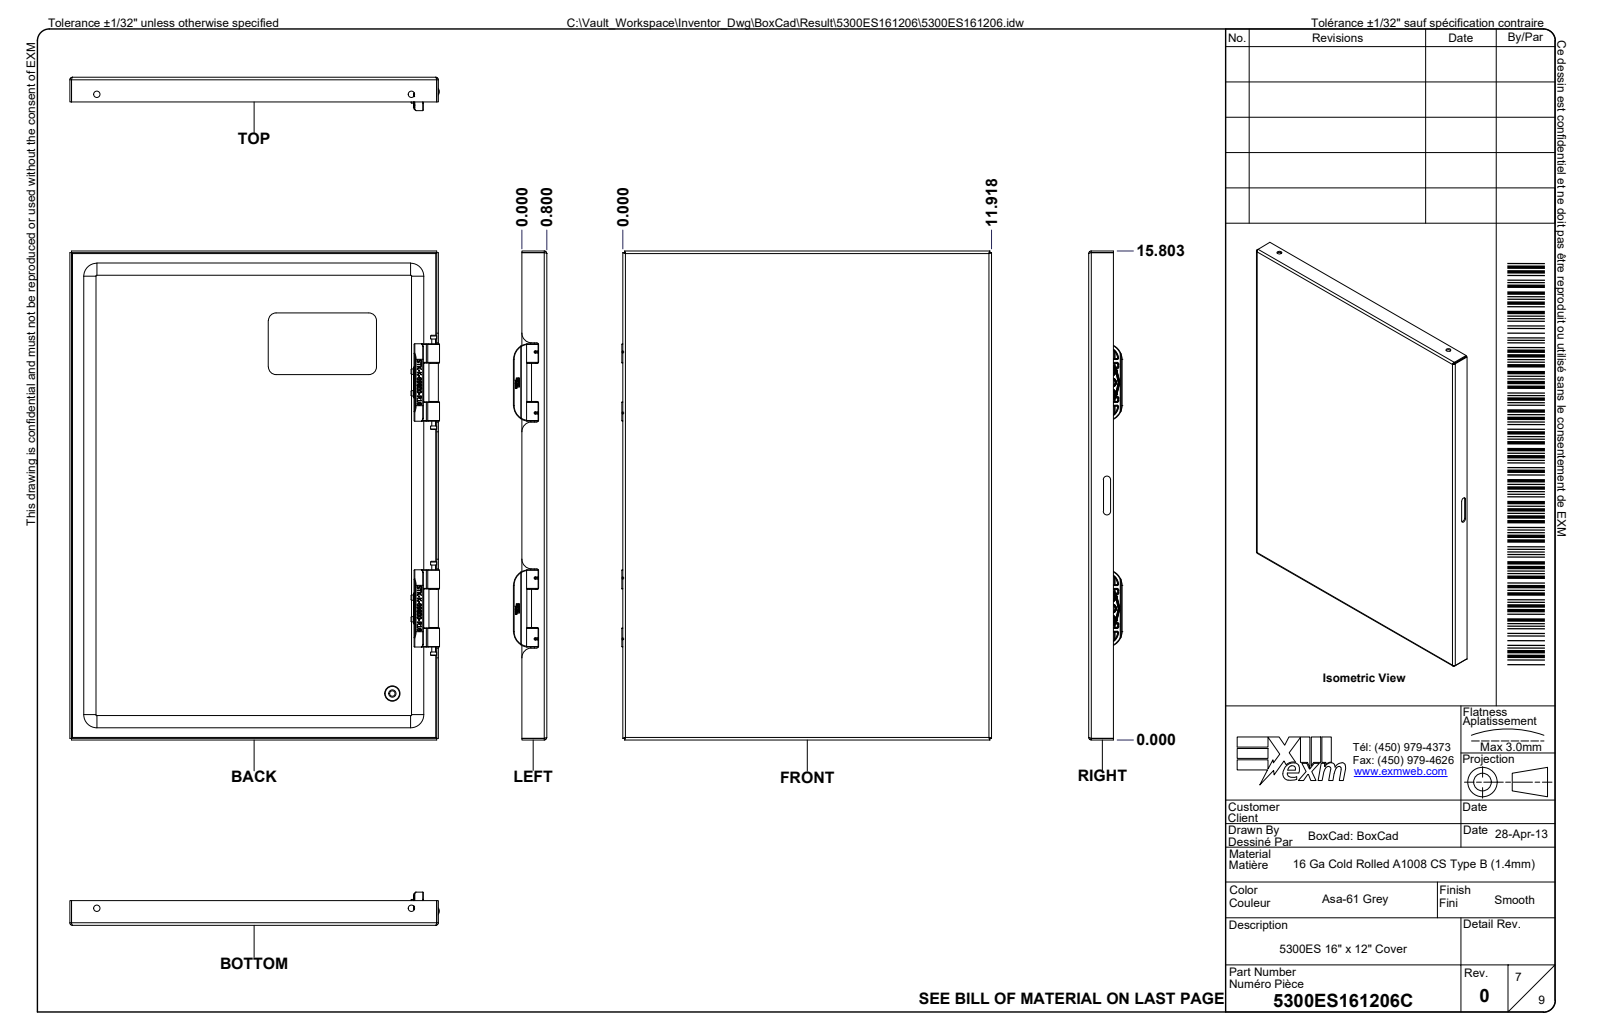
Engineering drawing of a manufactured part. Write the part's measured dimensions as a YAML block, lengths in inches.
part_name: "5300ES161206; 5300ES161206B; 5300ES161206B-P; STK-Q-16005 (+8 more)"
step_written_by: "Autodesk Inventor 2024 (AUTOMOTIVE_DESIGN)"
units: inches
bodies: {solids: 45, faces: 5491, planar: 1475, cylindrical: 1539, other: 2477}
overall_size: [16, 12.923, 7.104]
volume: 65.74
surface_area: 2117
round_holes:
  - {diameter: 0.043, count: 8}
  - {diameter: 0.03, count: 6}
  - {diameter: 0.315, count: 5}
  - {diameter: 0.178, count: 4}
  - {diameter: 0.27, count: 4}
  - {diameter: 0.29, count: 4}
  - {diameter: 0.39, count: 4}
  - {diameter: 0.201, count: 3}
  - {diameter: 0.187, count: 2}
  - {diameter: 0.203, count: 2}
  - {diameter: 0.22, count: 2}
  - {diameter: 0.33, count: 2}
round_bosses_or_shafts:
  - {diameter: 0.039, count: 8}
  - {diameter: 0.03, count: 6}
  - {diameter: 0.232, count: 5}
  - {diameter: 0.717, count: 4}
  - {diameter: 0.311, count: 4}
  - {diameter: 0.262, count: 4}
  - {diameter: 0.472, count: 2}
  - {diameter: 0.287, count: 2}
partial_cylinders:
  - {radius: 0.039, count: 85}
  - {radius: 0.02, count: 79}
  - {radius: 0.01, count: 66}
  - {radius: 0.008, count: 60}
  - {radius: 0.031, count: 36}
  - {radius: 0.016, count: 30}
  - {radius: 0.084, count: 28}
  - {radius: 0.004, count: 16}
face_to_face_distances: [0.053, 0.053, 6.998, 7.052, 11.947, 7.104, 7.051, 15.947, 0.927, 0.874]
hole_center_spacings: [7.303, 1, 8.25, 8.31, 9.442, 11.25, 13.422, 0.35]
